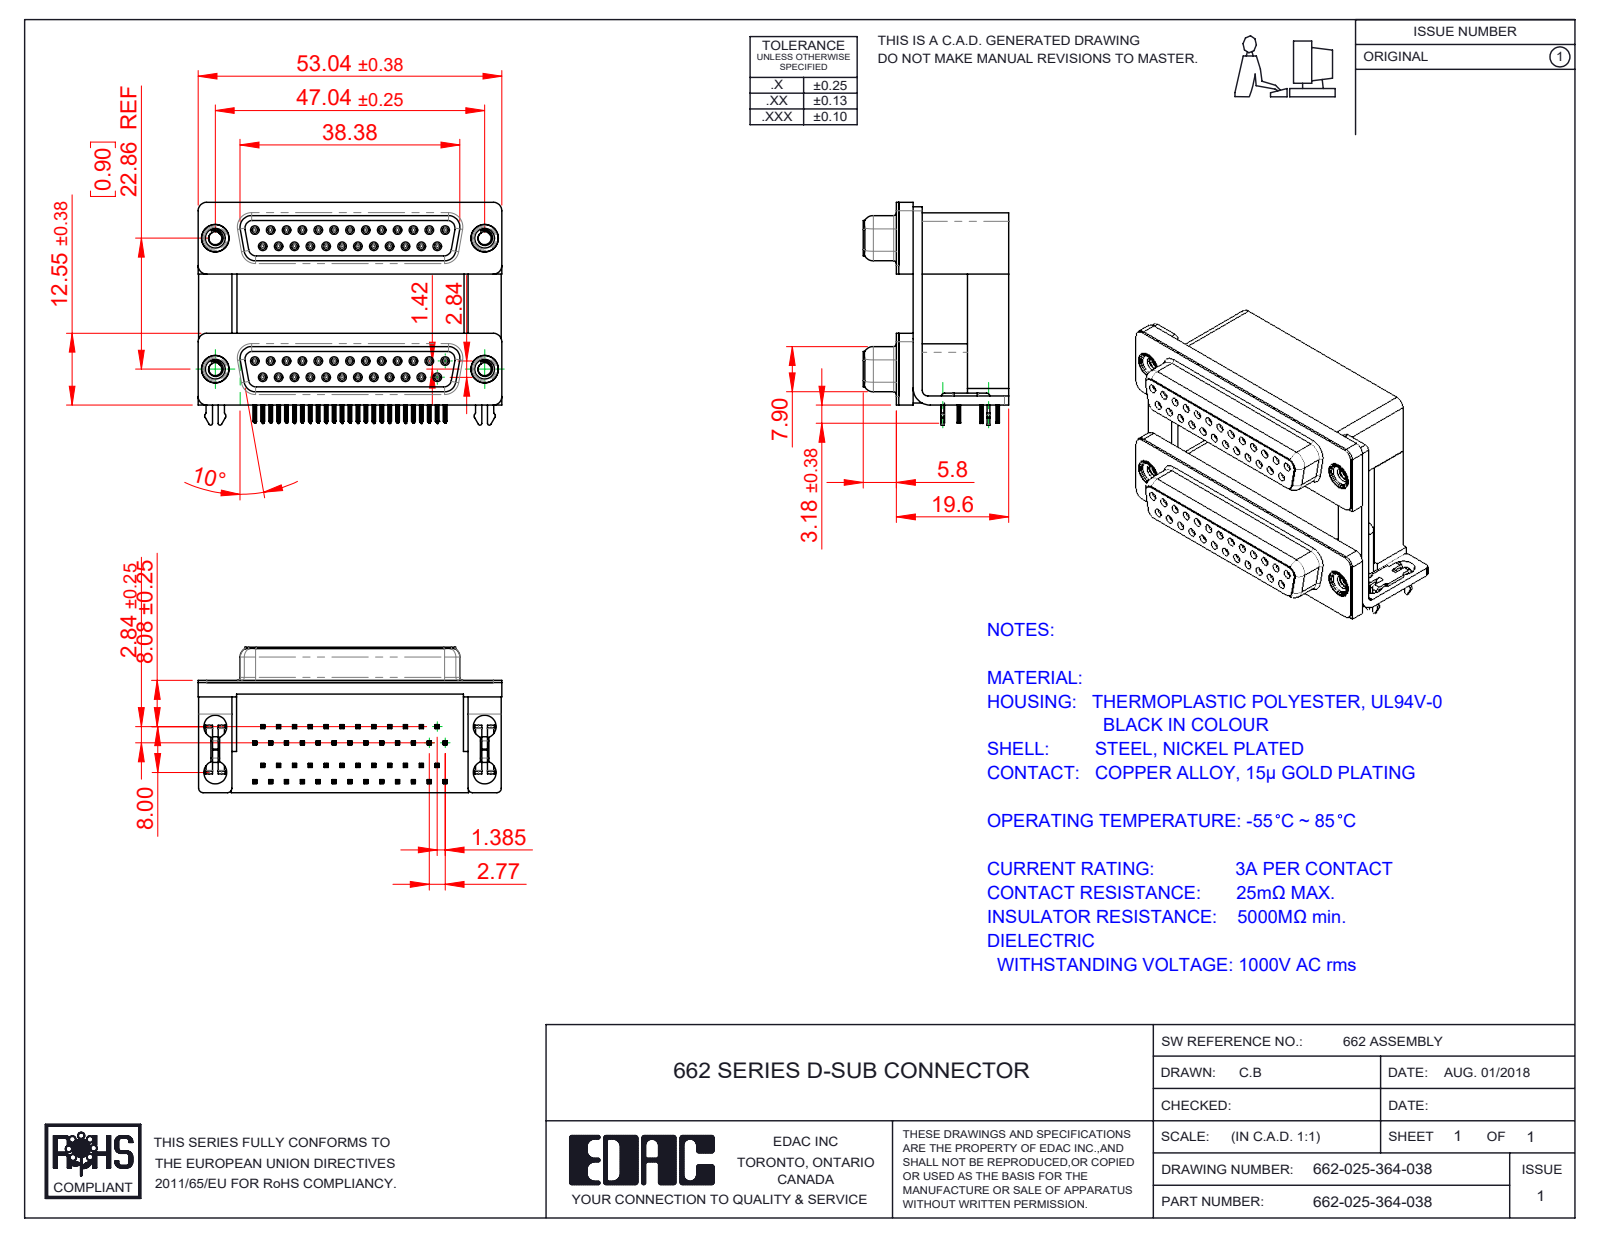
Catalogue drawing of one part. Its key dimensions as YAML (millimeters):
part_name: "662 2 Prong Board Lock_3; 662 Housing Lower_25 Contacts; 662 Contact Top Upper_H; 662 Shell_25 Contacts (+8 more)"
step_written_by: "SolidWorks 2020 (CONFIG_CONTROL_DESIGN)"
units: millimeters
bodies: {solids: 63, faces: 7944, planar: 3678, cylindrical: 1854, other: 2412}
overall_size: [53.04, 38.91, 25.4]
volume: 24994
surface_area: 27141
round_holes:
  - {diameter: 0.8, count: 50}
  - {diameter: 0.9, count: 50}
  - {diameter: 4, count: 8}
  - {diameter: 2.26, count: 4}
  - {diameter: 3.5, count: 4}
  - {diameter: 4.8, count: 4}
  - {diameter: 5, count: 4}
round_bosses_or_shafts:
  - {diameter: 1.2, count: 50}
  - {diameter: 4.9, count: 4}
  - {diameter: 4.75, count: 4}
  - {diameter: 3.9, count: 4}
partial_cylinders:
  - {radius: 0.1, count: 402}
  - {radius: 0.15, count: 200}
  - {radius: 0.35, count: 100}
  - {radius: 0.34, count: 50}
  - {radius: 0.28, count: 24}
  - {radius: 1.35, count: 16}
  - {radius: 1.5, count: 14}
  - {radius: 0.5, count: 12}
face_to_face_distances: [22.86, 19.2, 7.2, 12, 0.4, 10.7, 2.84, 6.2, 9.5, 16.7]
hole_center_spacings: [3.16, 2.77, 5.54, 11.08, 8.31, 5.03, 13.85, 7.48]
